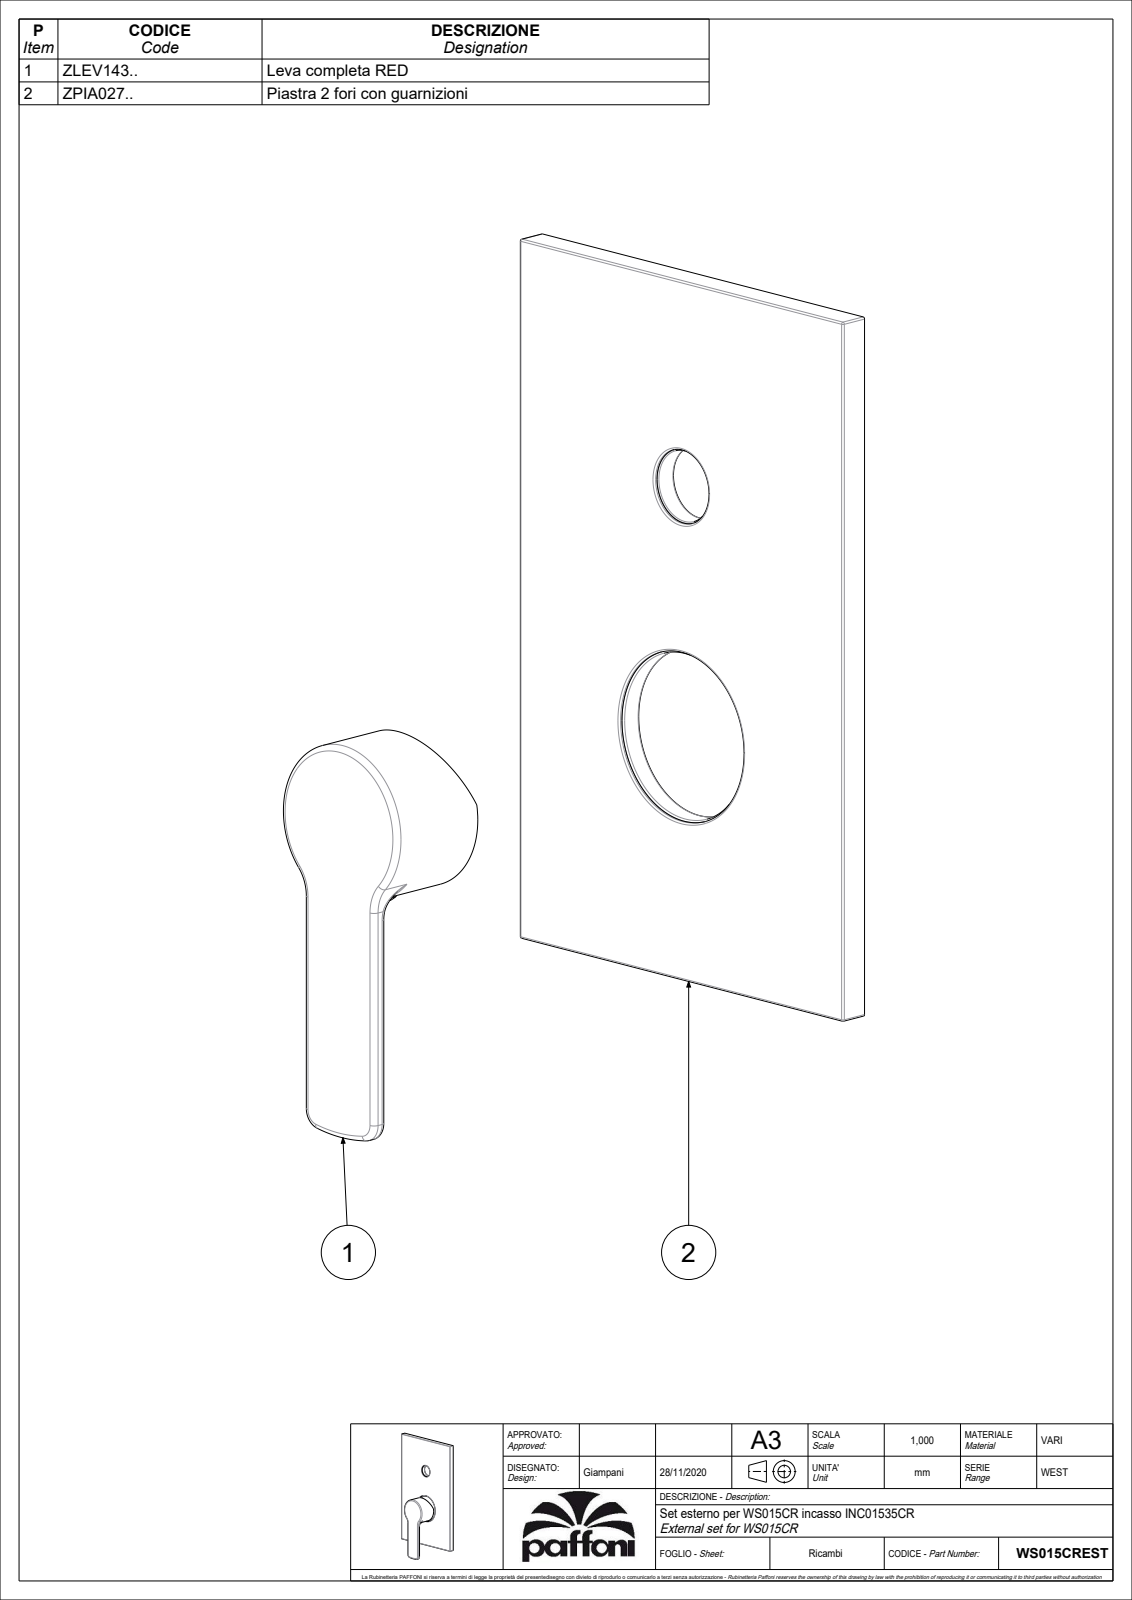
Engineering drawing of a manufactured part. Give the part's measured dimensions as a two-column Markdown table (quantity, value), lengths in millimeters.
| quantity | value |
| --- | --- |
| part name | WS015CREST |
| STEP written by | CREO PARAMETRIC BY PTC INC, 2020044 (CONFIG_CONTROL_DESIGN) |
| units | millimeters |
| bodies | 2 solids, 317 faces (87 planar, 113 cylindrical, 117 other) |
| overall size | 209 × 120 × 40.23 |
| volume | 136 601 mm³ |
| surface area | 69 814 mm² |
| round holes (diameter × count) | 3 × 1, 3.3 × 1, 4.5 × 1, 19.2 × 1, 20 × 1, 23.2 × 1, 45 × 1, 46 × 1 |
| round bosses / shafts (diameter × count) | 51 × 1, 49 × 1, 43 × 1, 25 × 1, 23 × 1, 7.6 × 1, 5.5 × 1, 5 × 1 |
| partial cylindrical surfaces (radius × count) | 0.5 × 47, 1 × 8, 1.5 × 4, 5 × 2, 10 × 2, 50 × 1 |
| main face-to-face distances | 7.5, 2.5, 5, 0.5, 22.5, 34.5, 30, 35, 4.5, 27.5 |
| hole center spacings | 68 |
